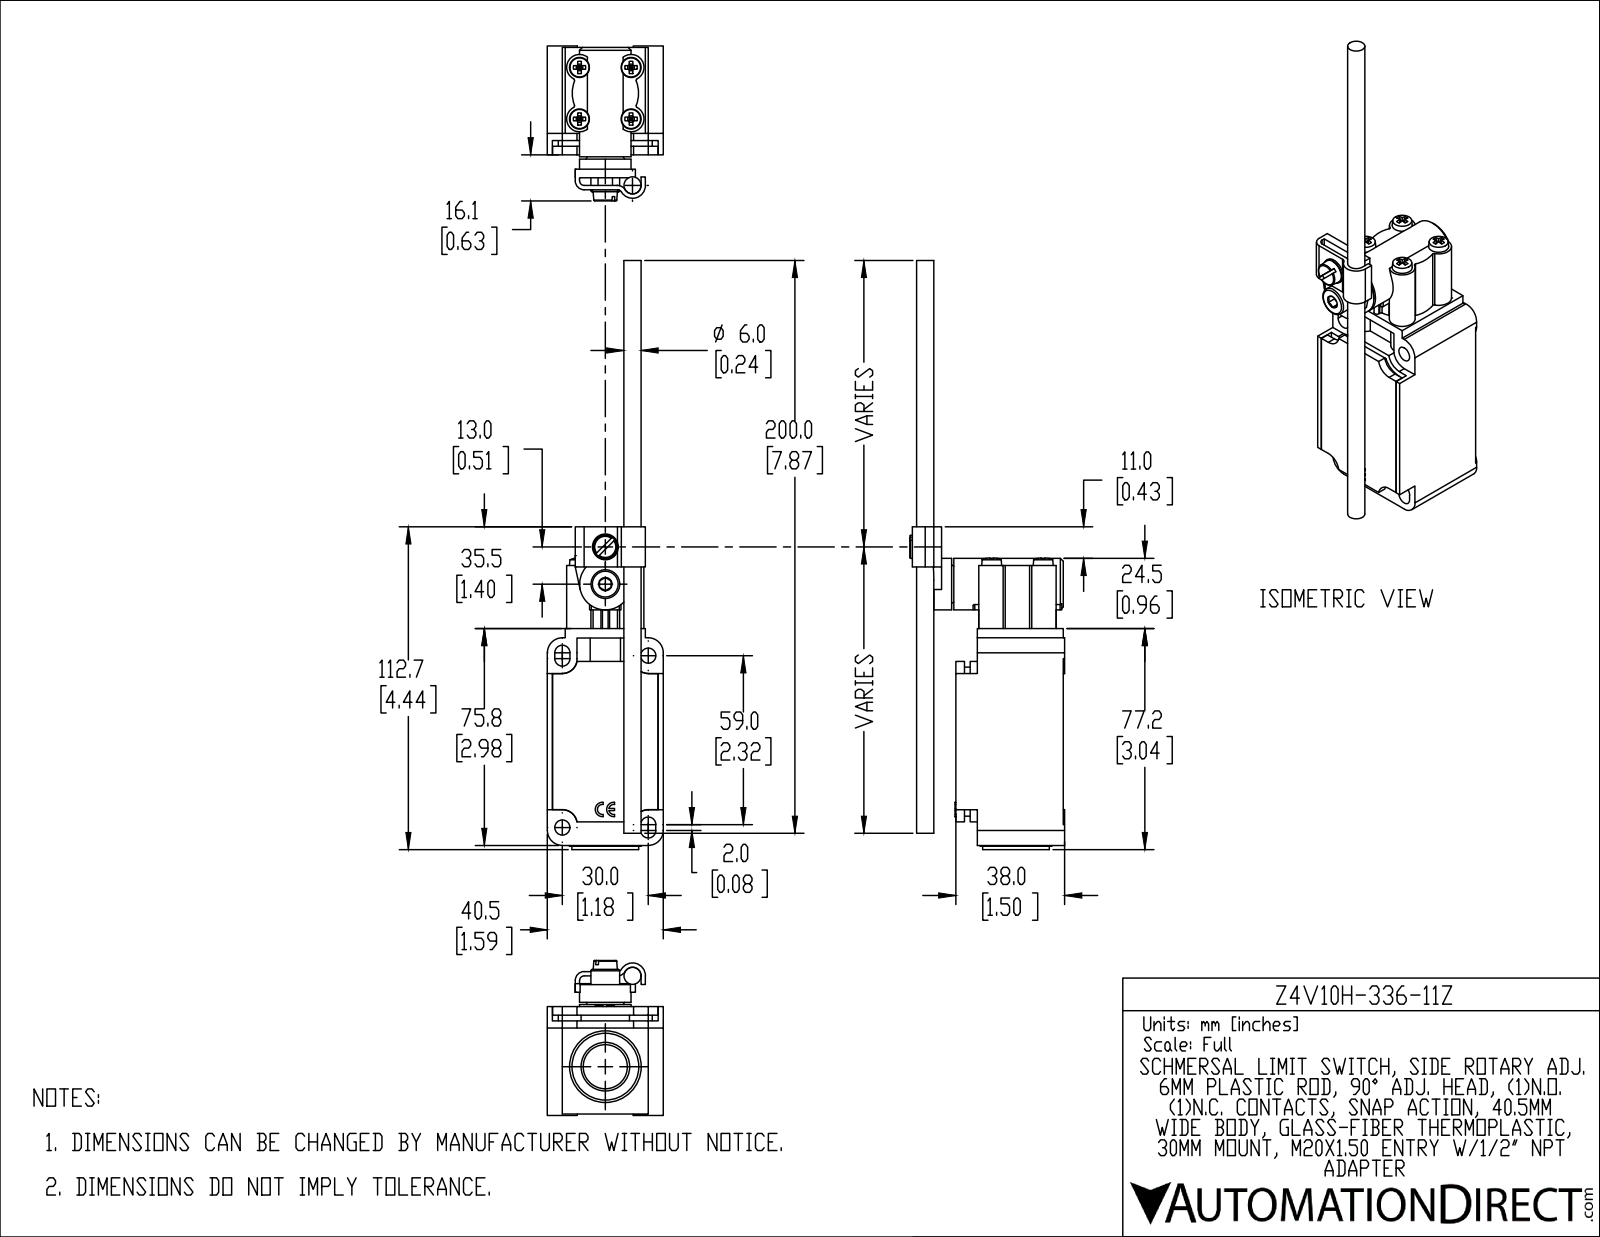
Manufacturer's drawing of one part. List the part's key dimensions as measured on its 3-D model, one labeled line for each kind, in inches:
Part name (STEP PRODUCT): Z4V10H-336-11Z
STEP written by: SolidWorks 2019 (AUTOMOTIVE_DESIGN)
Units: inches
Bodies: 3 solids, 340 faces (238 planar, 79 cylindrical, 23 other)
Overall size (bounding box): 8.098 × 2.13 × 1.594
Volume: 7.781 in³ · Surface area: 46.35 in²
Round holes (diameter × count): ⌀0.209 ×2, ⌀0.236 ×1, ⌀0.65 ×1, ⌀0.669 ×1
Round bosses / shafts (diameter × count): ⌀0.984 ×1, ⌀0.917 ×1, ⌀0.709 ×1, ⌀0.394 ×1, ⌀0.354 ×1, ⌀0.197 ×1
Partial cylindrical surfaces — rounded edges, fillets, slot ends (radius × count): R0.024 ×16, R0.205 ×8, R0.207 ×8, R0.177 ×5, R0.104 ×4, R0.283 ×4, R0.039 ×2, R0.063 ×2
Main face-to-face distances: 1.594, 1.476, 0.177, 0.315, 1.181, 0.197, 0.295, 0.118, 0.079, 1.28
Hole centre spacings: 1.148, 1.303, 2.641, 3.398
